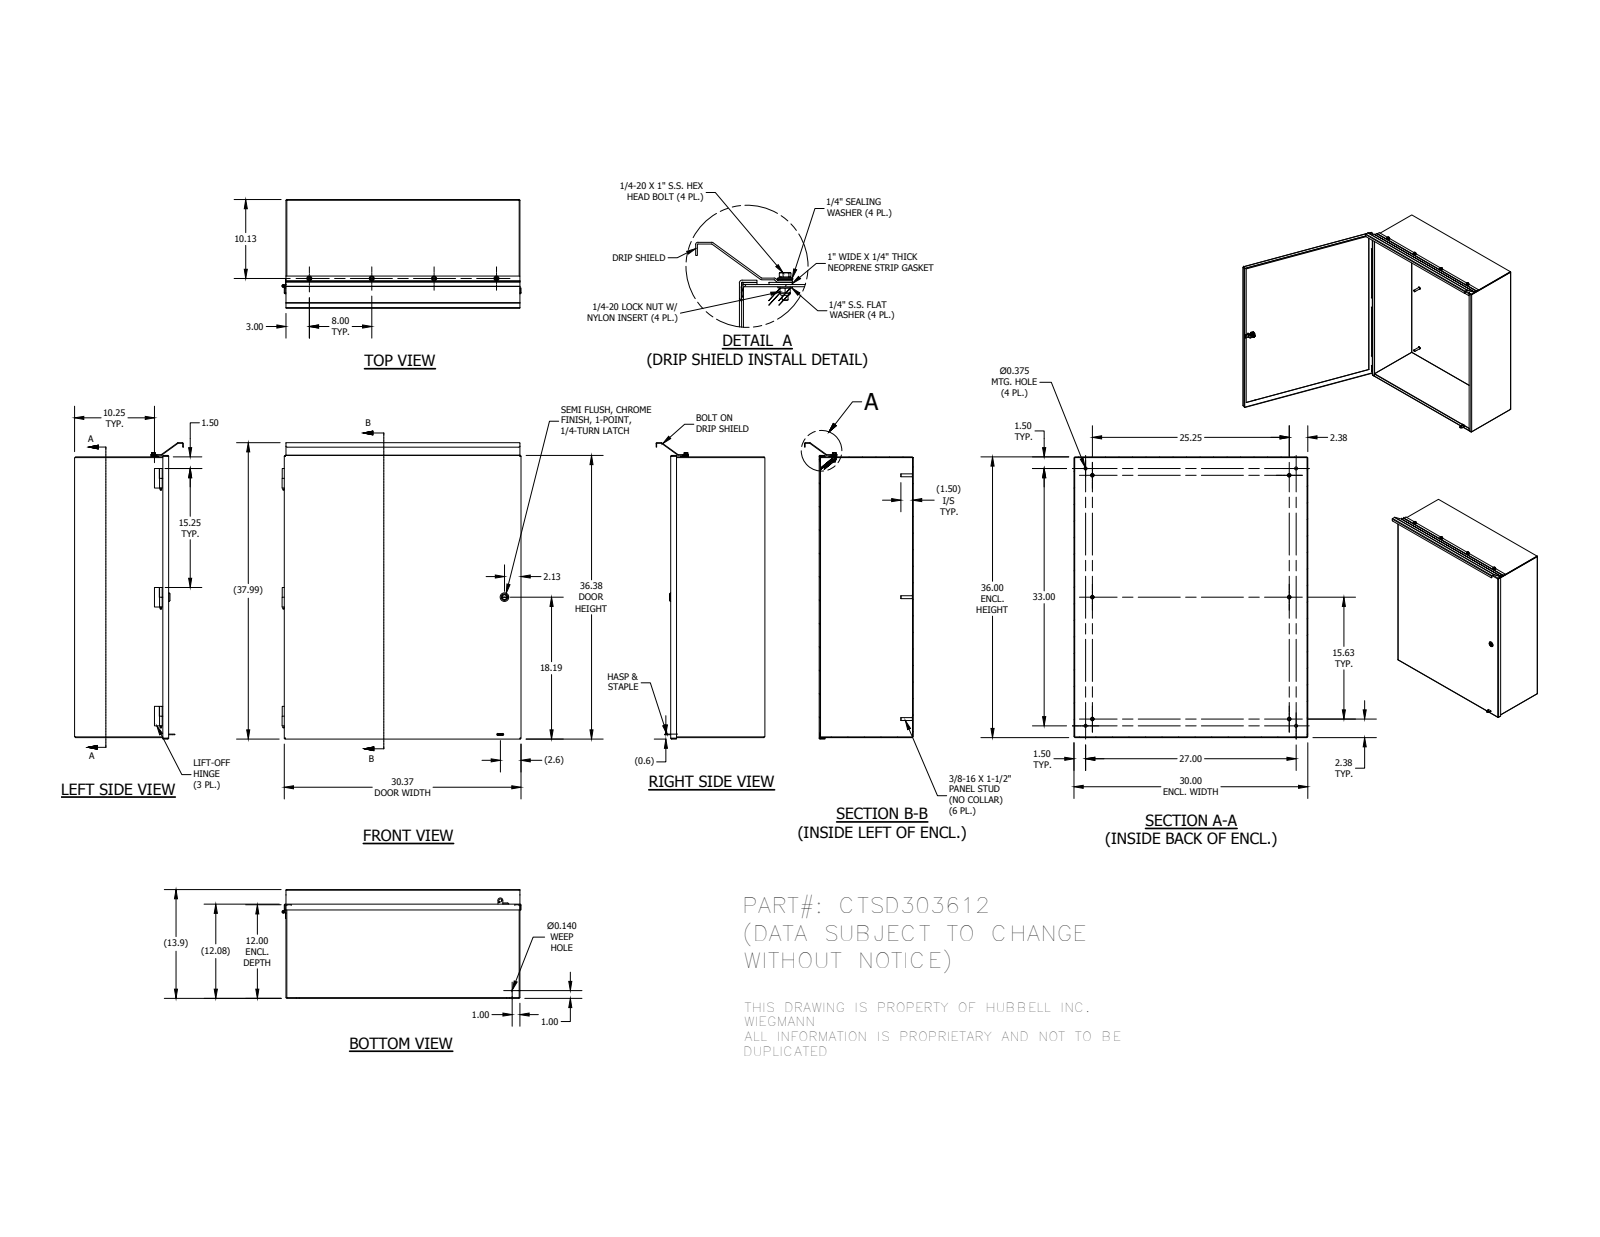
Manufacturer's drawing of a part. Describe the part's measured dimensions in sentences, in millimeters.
The part is named "CTSD303612BLR; CTSD3012TOP; CTSD3012BTM; 31815 (+8 more)". Its 3-D file was written by "Autodesk Inventor 2014 (AUTOMOTIVE_DESIGN)". It is 47 solids with 972 faces: 548 planar, 270 cylindrical and 154 other. Overall it measures 965.07 by 778.38 by 354.32 millimeters. Its volume is 6 349 000 cubic millimeters and its surface area 5 465 000 square millimeters. Round holes: 6 of diameter 7.14, 5 of diameter 9.52, 4 of diameter 4.98, 4 of diameter 5.97, 4 of diameter 6.99, 4 of diameter 7.37, 1 of diameter 3.17, 1 of diameter 3.56, 1 of diameter 5, 1 of diameter 5.36, 1 of diameter 5.56, 1 of diameter 8. Round bosses or shafts: 6 of diameter 11.73, 6 of diameter 9.52, 4 of diameter 16.51, 4 of diameter 15.88, 4 of diameter 15.24, 4 of diameter 11.13, 4 of diameter 11.05, 4 of diameter 6.6. Partial cylindrical surfaces (rounded edges, fillets, slot ends): 30 of radius 0.3, 18 of radius 0.79, 10 of radius 0.5, 10 of radius 3.17, 6 of radius 2.67, 4 of radius 3.17, 4 of radius 4, 3 of radius 0.4. The main face-to-face distances are 2.38, 304.4, 302.02, 306.78, 759.62, 912.02, 914.4, 757.24, 762, 909.64. The hole center spacings are 203.2, 406.4, 62.92, 218.46, 224.52, 288.75, 418.12, 419.28.
